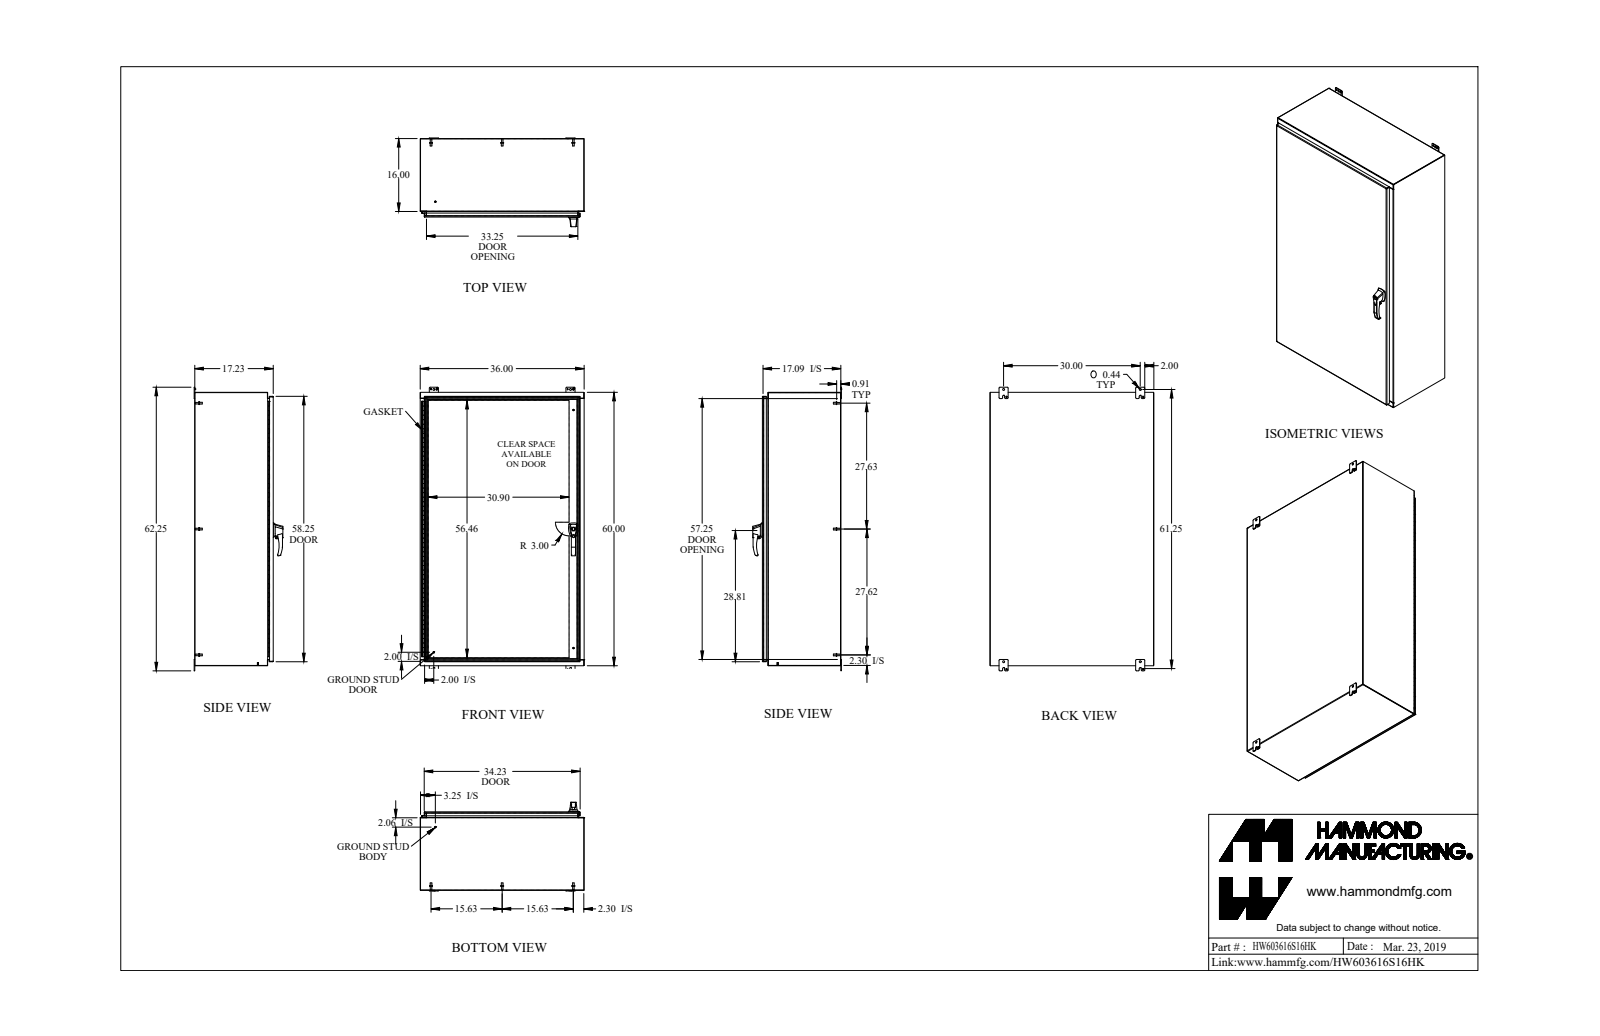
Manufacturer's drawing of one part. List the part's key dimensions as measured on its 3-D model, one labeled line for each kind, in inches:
Part name (STEP PRODUCT): HW603616S16HK
STEP written by: SolidWorks 2018 (AUTOMOTIVE_DESIGN)
Units: inches
Bodies: 47 solids, 1692 faces (778 planar, 778 cylindrical, 136 other)
Overall size (bounding box): 62.25 × 36 × 19.473
Volume: 664.3 in³ · Surface area: 16 657 in²
Round holes (diameter × count): ⌀0.176 ×6, ⌀0.313 ×4, ⌀0.25 ×3, ⌀0.265 ×3, ⌀0.413 ×3, ⌀0.196 ×2, ⌀0.256 ×2, ⌀0.394 ×2, ⌀0.437 ×2, ⌀0.11 ×1, ⌀0.233 ×1, ⌀0.33 ×1
Round bosses / shafts (diameter × count): ⌀0.375 ×13, ⌀0.65 ×8, ⌀0.332 ×8, ⌀0.25 ×7, ⌀0.156 ×6, ⌀1 ×3, ⌀0.63 ×2, ⌀0.51 ×2
Partial cylindrical surfaces — rounded edges, fillets, slot ends (radius × count): R0.25 ×27, R0.188 ×24, R0.036 ×14, R0.108 ×14, R0.06 ×12, R0.125 ×9, R0.218 ×8, R0.03 ×6
Main face-to-face distances: 0.072, 17.138, 17.066, 0.095, 17.233, 17.161, 35.928, 59.928, 35.856, 36
Hole centre spacings: 26.118, 26.119, 30, 52.237, 1.11, 1.111, 26.119, 26.884
